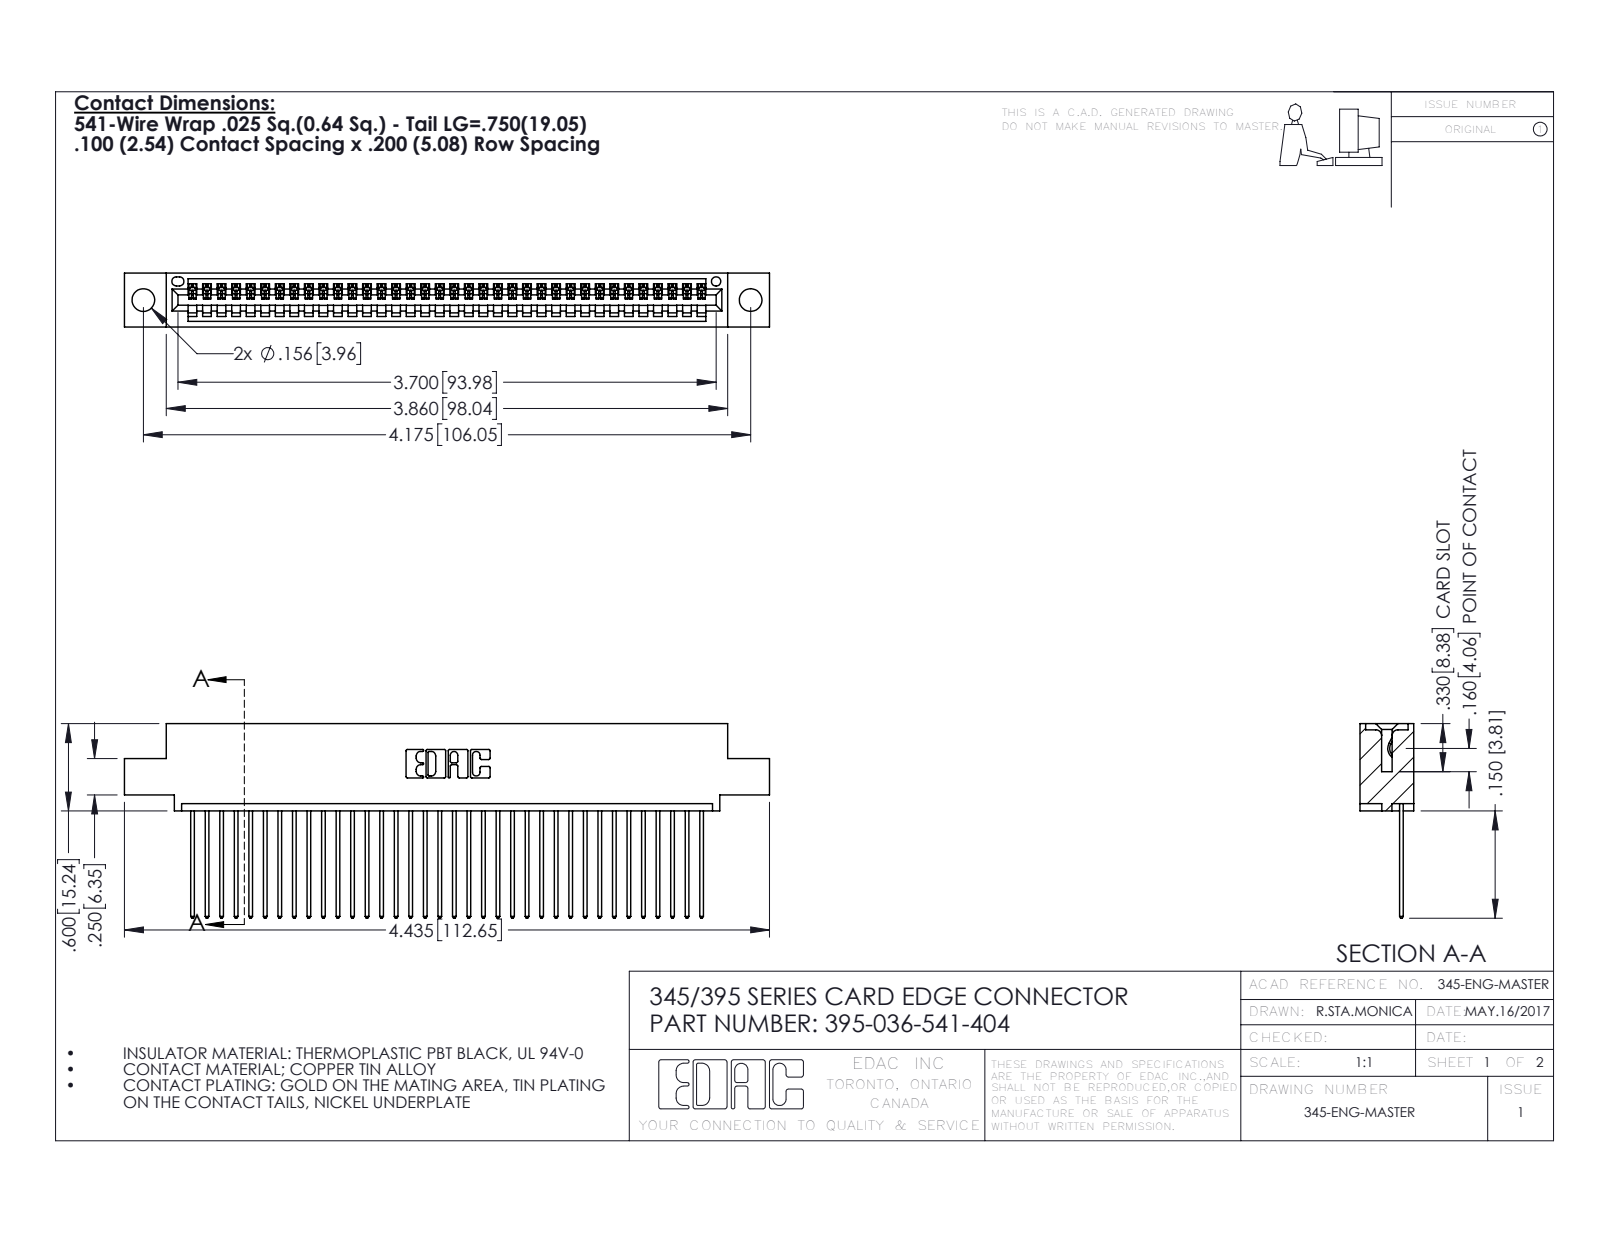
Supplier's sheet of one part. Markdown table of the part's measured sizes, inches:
| quantity | value |
| --- | --- |
| part name | 395-036-541-404; 345 Part_0.110 Offset - 0.156 Dia-TH; 345-292-001_345-293-141 |
| STEP written by | SolidWorks 2016 (CONFIG_CONTROL_DESIGN) |
| units | inches |
| bodies | 37 solids, 2218 faces (1524 planar, 694 cylindrical, 0 other) |
| overall size | 4.435 × 1.337 × 0.37 |
| volume | 0.647 in³ |
| surface area | 22.64 in² |
| round holes (diameter × count) | 0.156 × 2, 0.064 × 1 |
| partial cylindrical surfaces (radius × count) | 0.006 × 72, 0.01 × 72, 0.01 × 22, 0.007 × 6, 0.031 × 6, 0.026 × 3, 0.031 × 2, 0.04 × 2 |
| main face-to-face distances | 0.072, 0.298, 0.098, 0.272, 0.025, 0.37, 0.2, 0.225, 0.149, 0.072 |
| hole center spacings | 0.27, 3.939, 4.175 |
